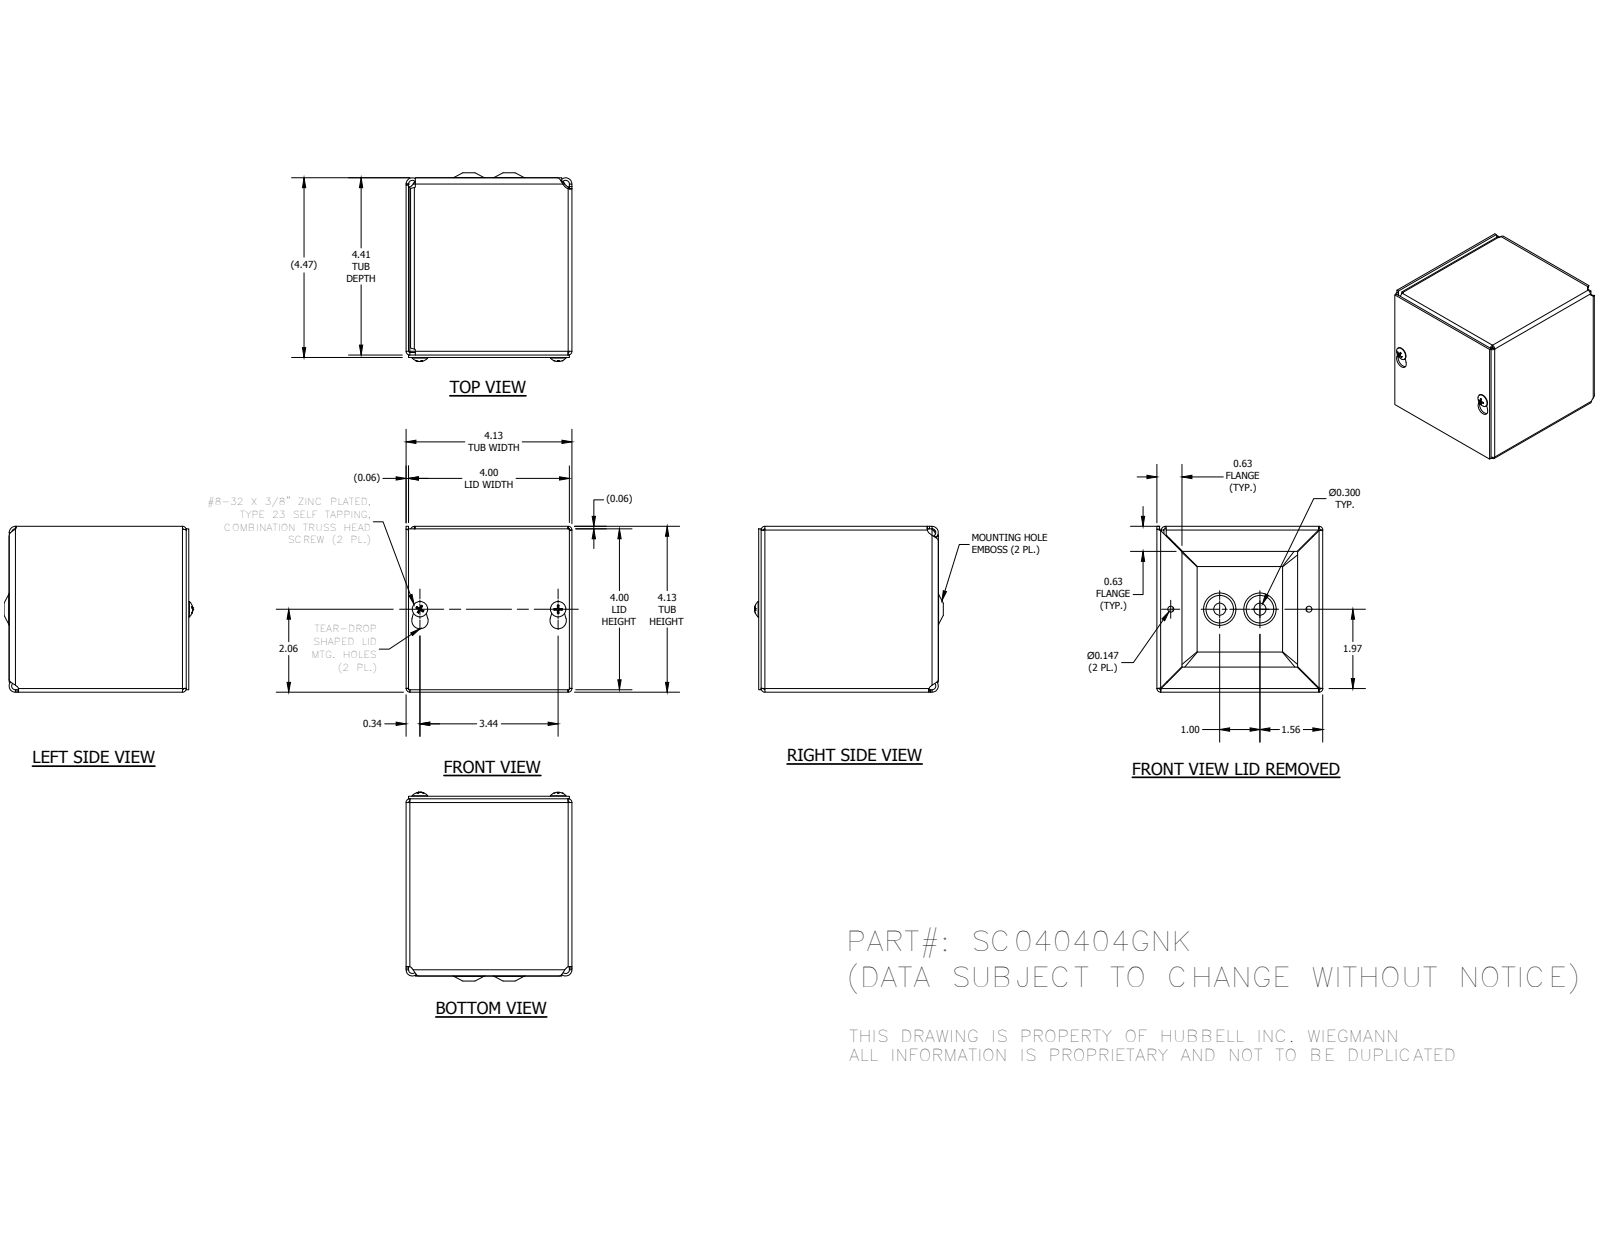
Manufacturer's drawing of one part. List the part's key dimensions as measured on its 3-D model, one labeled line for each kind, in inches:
Part name (STEP PRODUCT): SC0404GNKBKP; SC040404GNKWRA; SC0404GNKLID; 34056 (+1 more)
STEP written by: Autodesk Inventor 2014 (AUTOMOTIVE_DESIGN)
Units: inches
Bodies: 5 solids, 275 faces (108 planar, 59 cylindrical, 108 other)
Overall size (bounding box): 4.693 × 4.125 × 4.125
Volume: 7.43 in³ · Surface area: 244.9 in²
Round holes (diameter × count): ⌀0.147 ×2, ⌀0.3 ×2
Round bosses / shafts (diameter × count): ⌀0.384 ×2, ⌀0.164 ×2
Partial cylindrical surfaces — rounded edges, fillets, slot ends (radius × count): R0.031 ×8, R0.093 ×8, R0.055 ×4, R0.062 ×4, R0.094 ×4, R0.117 ×4, R0.124 ×4, R0.156 ×4
Main face-to-face distances: 0.062, 0.062, 4.063, 4.125, 4.001, 4.063, 4.343, 4.405, 0.063, 4.406
Hole centre spacings: 1, 1.219, 1.219, 2.219, 2.219, 3.437
